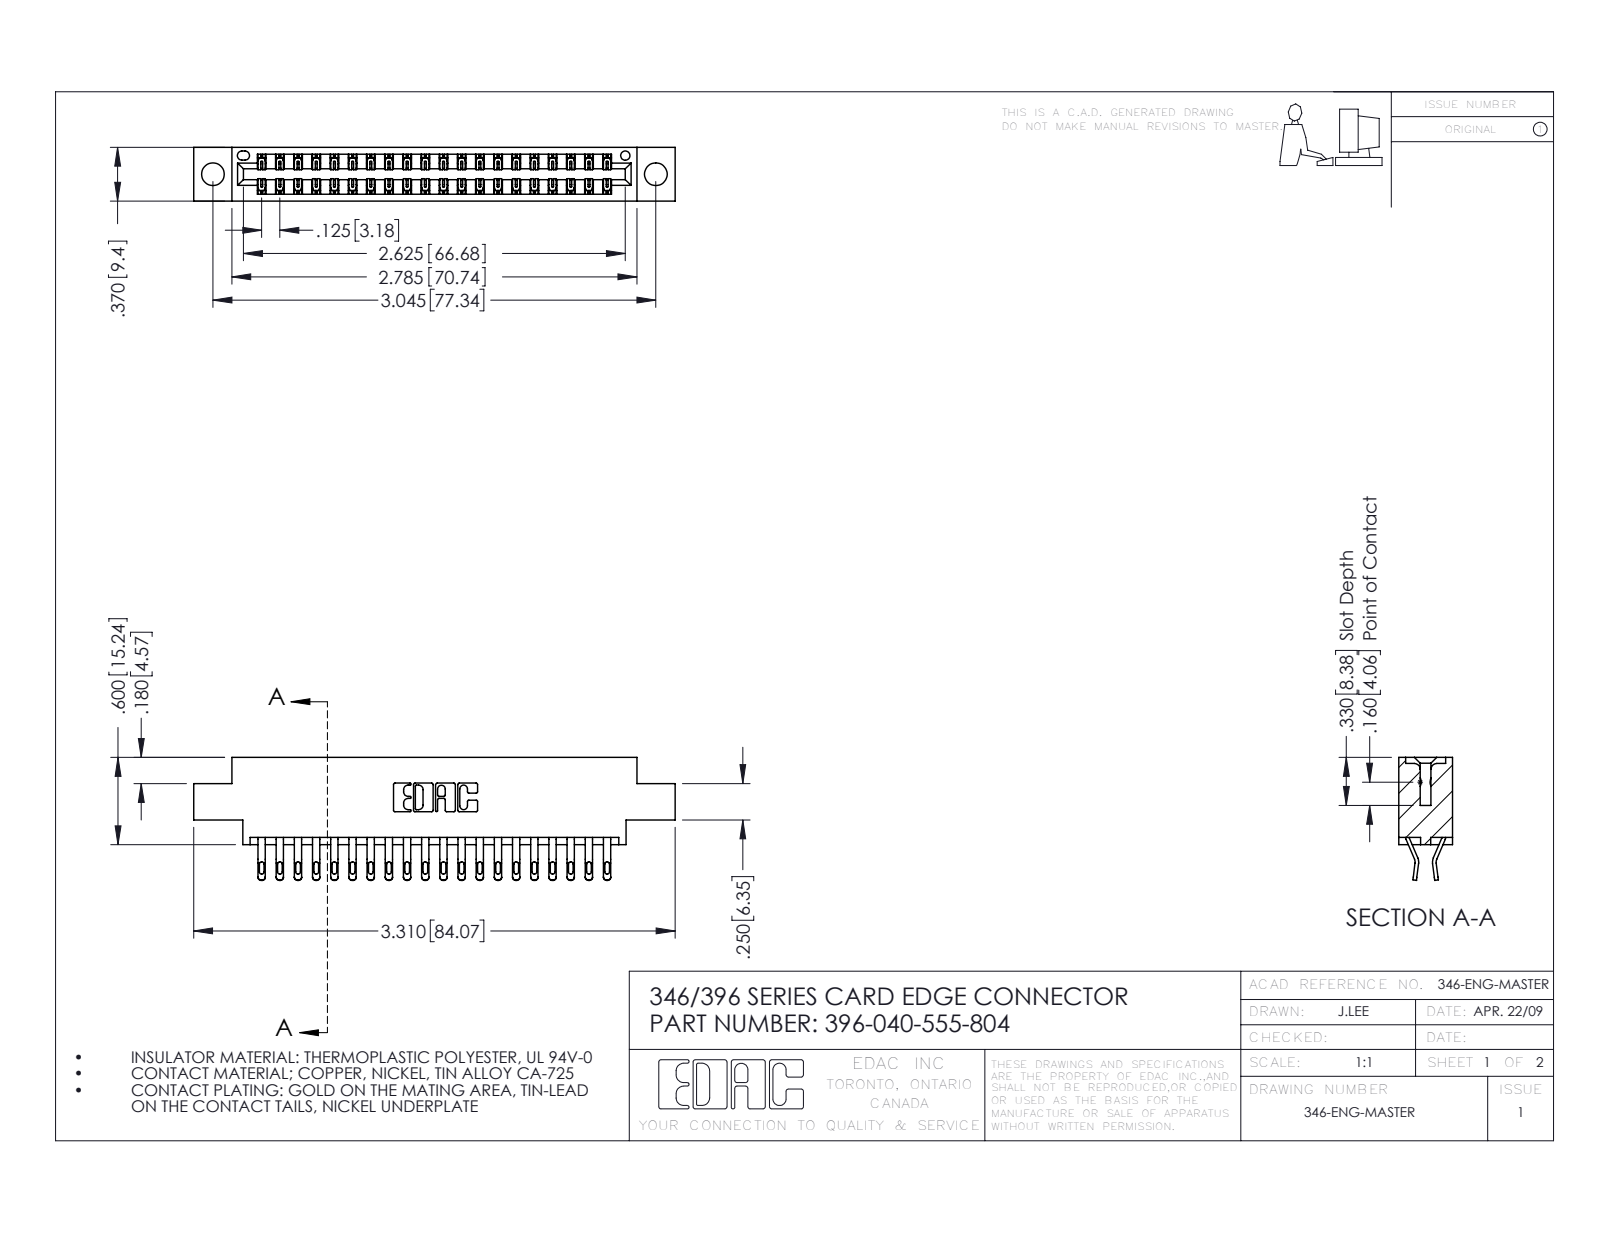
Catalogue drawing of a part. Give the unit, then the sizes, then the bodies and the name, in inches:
Units: inches
Overall size (bounding box): 3.31 × 0.845 × 0.37
Round holes (diameter × count): ⌀0.156 ×2, ⌀0.064 ×1
Partial cylindrical surfaces — rounded edges, fillets, slot ends (radius × count): R0.016 ×80, R0.02 ×80, R0.006 ×60, R0.01 ×22, R0.007 ×6, R0.031 ×6, R0.026 ×3, R0.01 ×2
Main face-to-face distances: 0.048, 0.322, 0.37, 0.25, 0.025, 0.072, 0.298, 0.275, 0.148, 0.222
Hole centre spacings: 0.246, 2.837, 3.045
Volume: 0.482 in³ · Surface area: 16.93 in²
Bodies: 41 solids, 2446 faces (1400 planar, 1046 cylindrical, 0 other)
Part name (STEP PRODUCT): 396-040-555-804; 345-292-001_555 Tail; 346 Part_0.170 Offset - 0.156 Dia-TH
STEP written by: SolidWorks 2016 (CONFIG_CONTROL_DESIGN)
